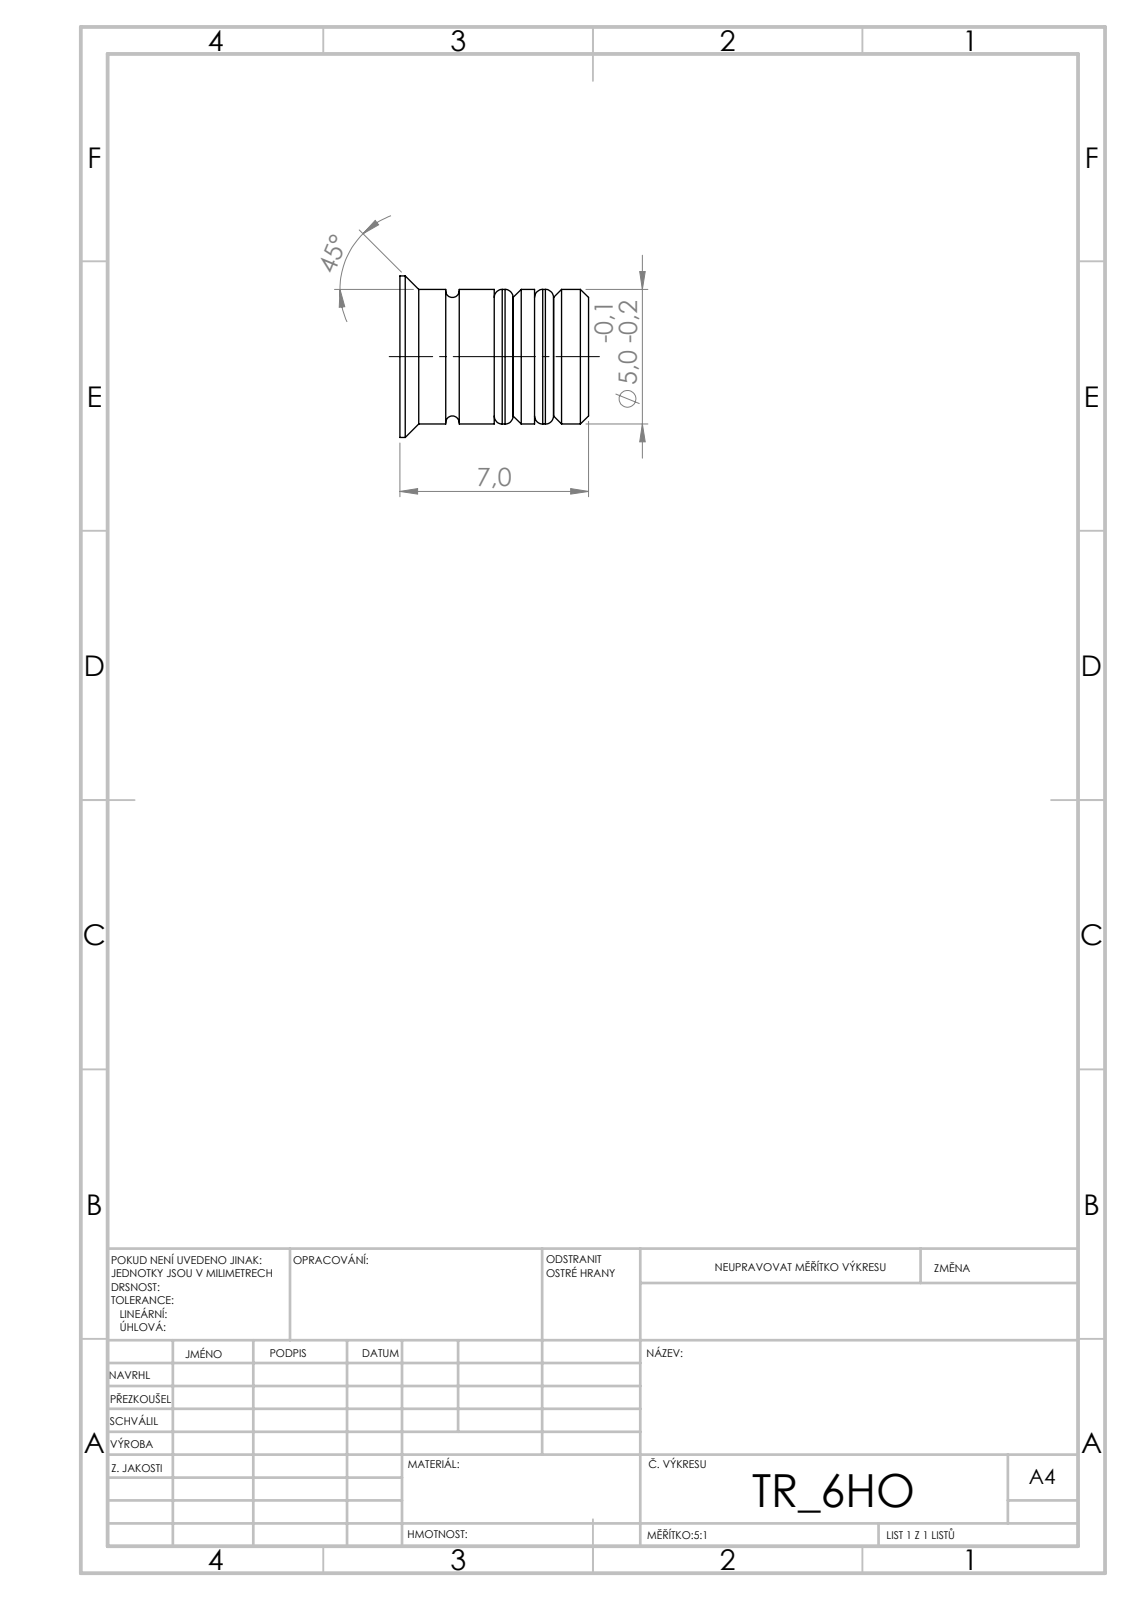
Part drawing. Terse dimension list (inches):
written by: SolidWorks 2019 (CONFIG_CONTROL_DESIGN)
unit: in
bodies: 3 solids, 67 faces (25 planar, 20 cylindrical, 22 other)
size: 0.276 × 0.236 × 0.236
volume: 0.009 in³; area: 0.443 in²
bosses: 1× ⌀0.236, 1× ⌀0.197, 1× ⌀0.173, 1× ⌀0.079
face distances: 0.138, 0.059, 0.028, 0.197, 0.079, 0.051, 0.087, 0.11, 0.276, 0.224
